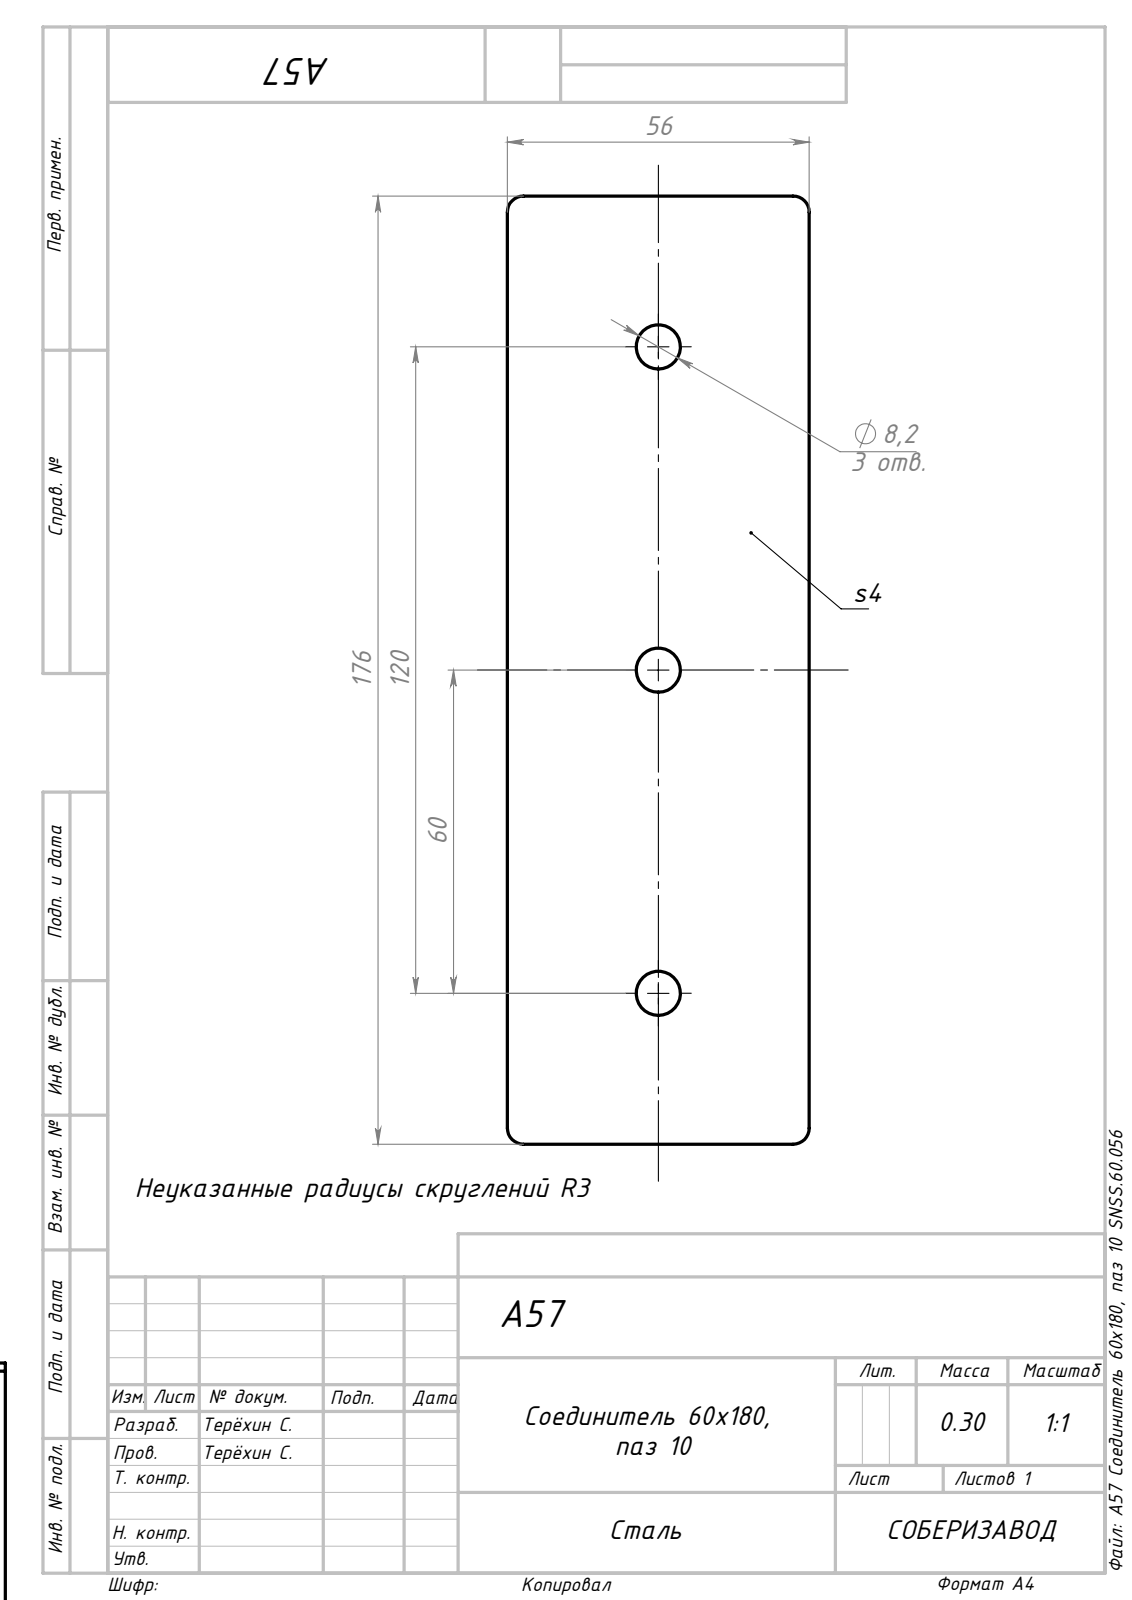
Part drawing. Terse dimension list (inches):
name: Сборка1; A57 Cоединитель 60x180, паз 10 SNSS.60.056_00
written by: SolidWorks 2022 (AUTOMOTIVE_DESIGN)
unit: in
bodies: 1 solid, 16 faces (6 planar, 10 cylindrical, 0 other)
size: 6.929 × 2.205 × 0.157
volume: 2.365 in³; area: 33.36 in²
holes: 3× ⌀0.323
rounds: 4× R0.118
face distances: 0.157, 2.205, 6.929
hole spacings: 2.362, 4.724
